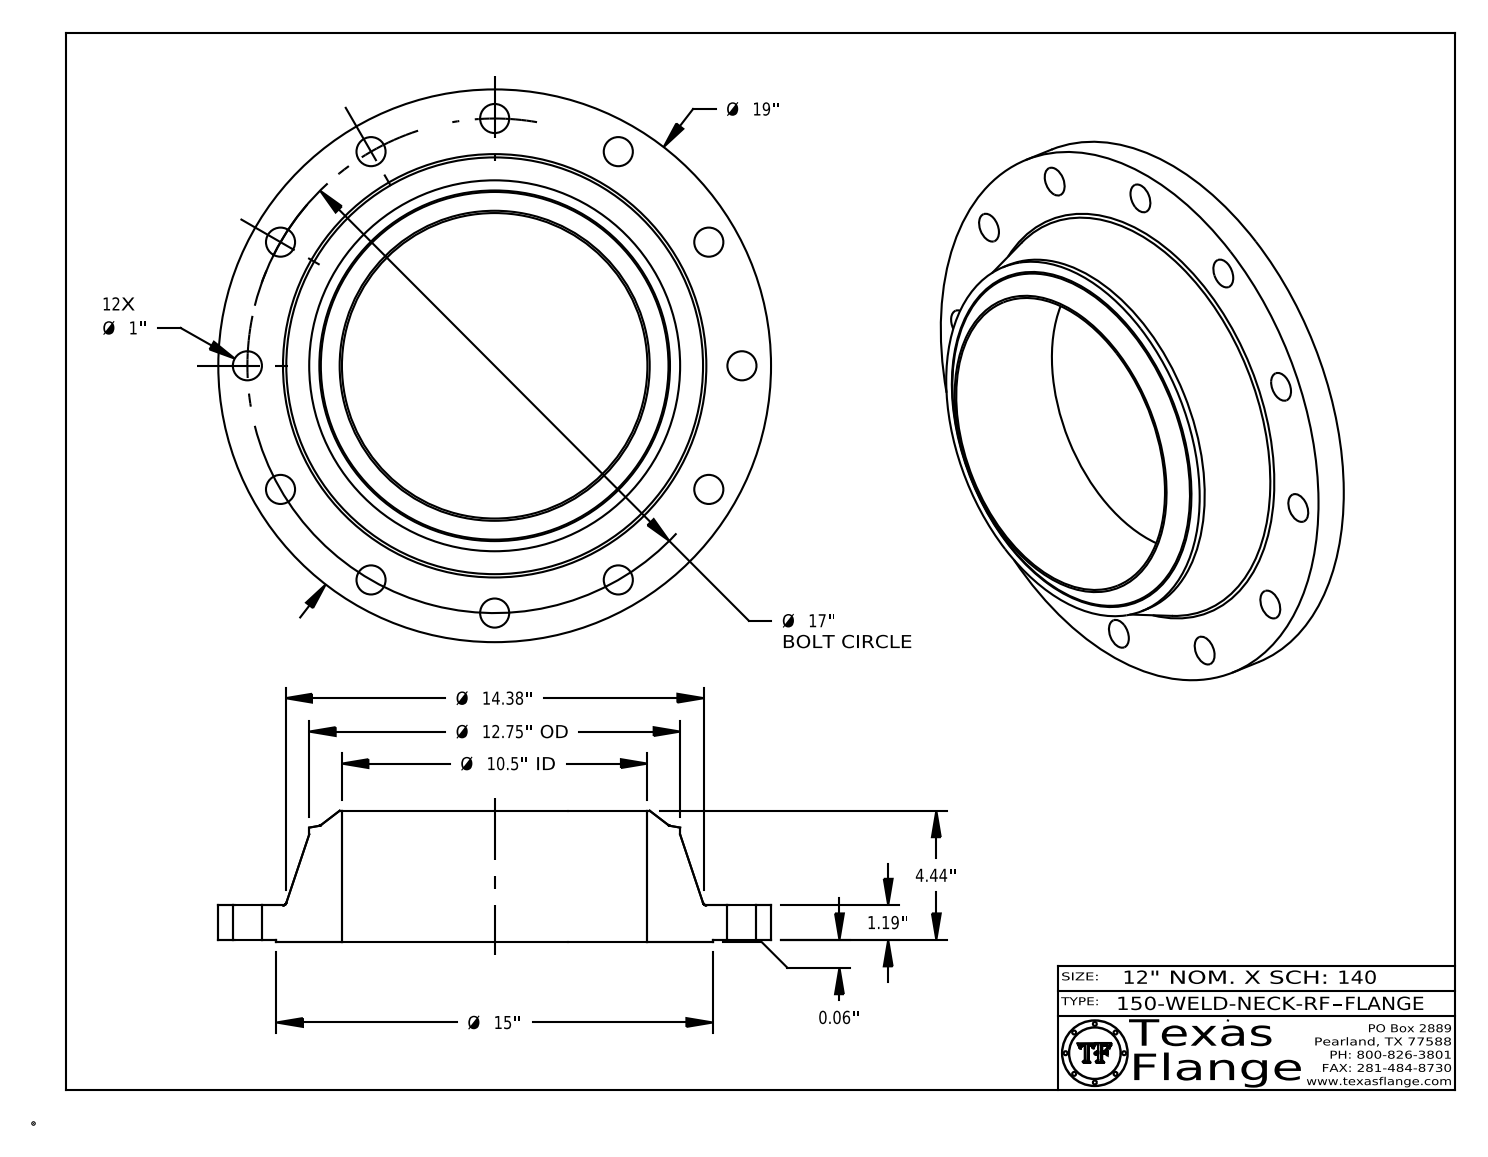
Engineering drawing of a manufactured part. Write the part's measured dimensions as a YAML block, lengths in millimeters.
part_name: "150-WELD-NECK-RF"
step_written_by: "CATIA V5 STEP AP214 (AUTOMOTIVE_DESIGN)"
units: millimeters
bodies: {solids: 1, faces: 431, planar: 369, cylindrical: 52, other: 10}
overall_size: [482.6, 482.6, 114.4]
volume: 6383000
surface_area: 472200
round_holes:
  - {diameter: 25.4, count: 12}
  - {diameter: 12.6, count: 1}
  - {diameter: 266.7, count: 1}
round_bosses_or_shafts:
  - {diameter: 0.8, count: 8}
  - {diameter: 482.6, count: 1}
  - {diameter: 381, count: 1}
  - {diameter: 323.9, count: 1}
  - {diameter: 9.9, count: 1}
face_to_face_distances: [30.2, 1.6, 31.8, 114.4, 112.8, 82.6, 0.4, 31.4, 29.8, 82.9]
hole_center_spacings: [215.9, 417.1, 111.8, 305.3, 373.9, 111.8, 305.3, 373.9]
